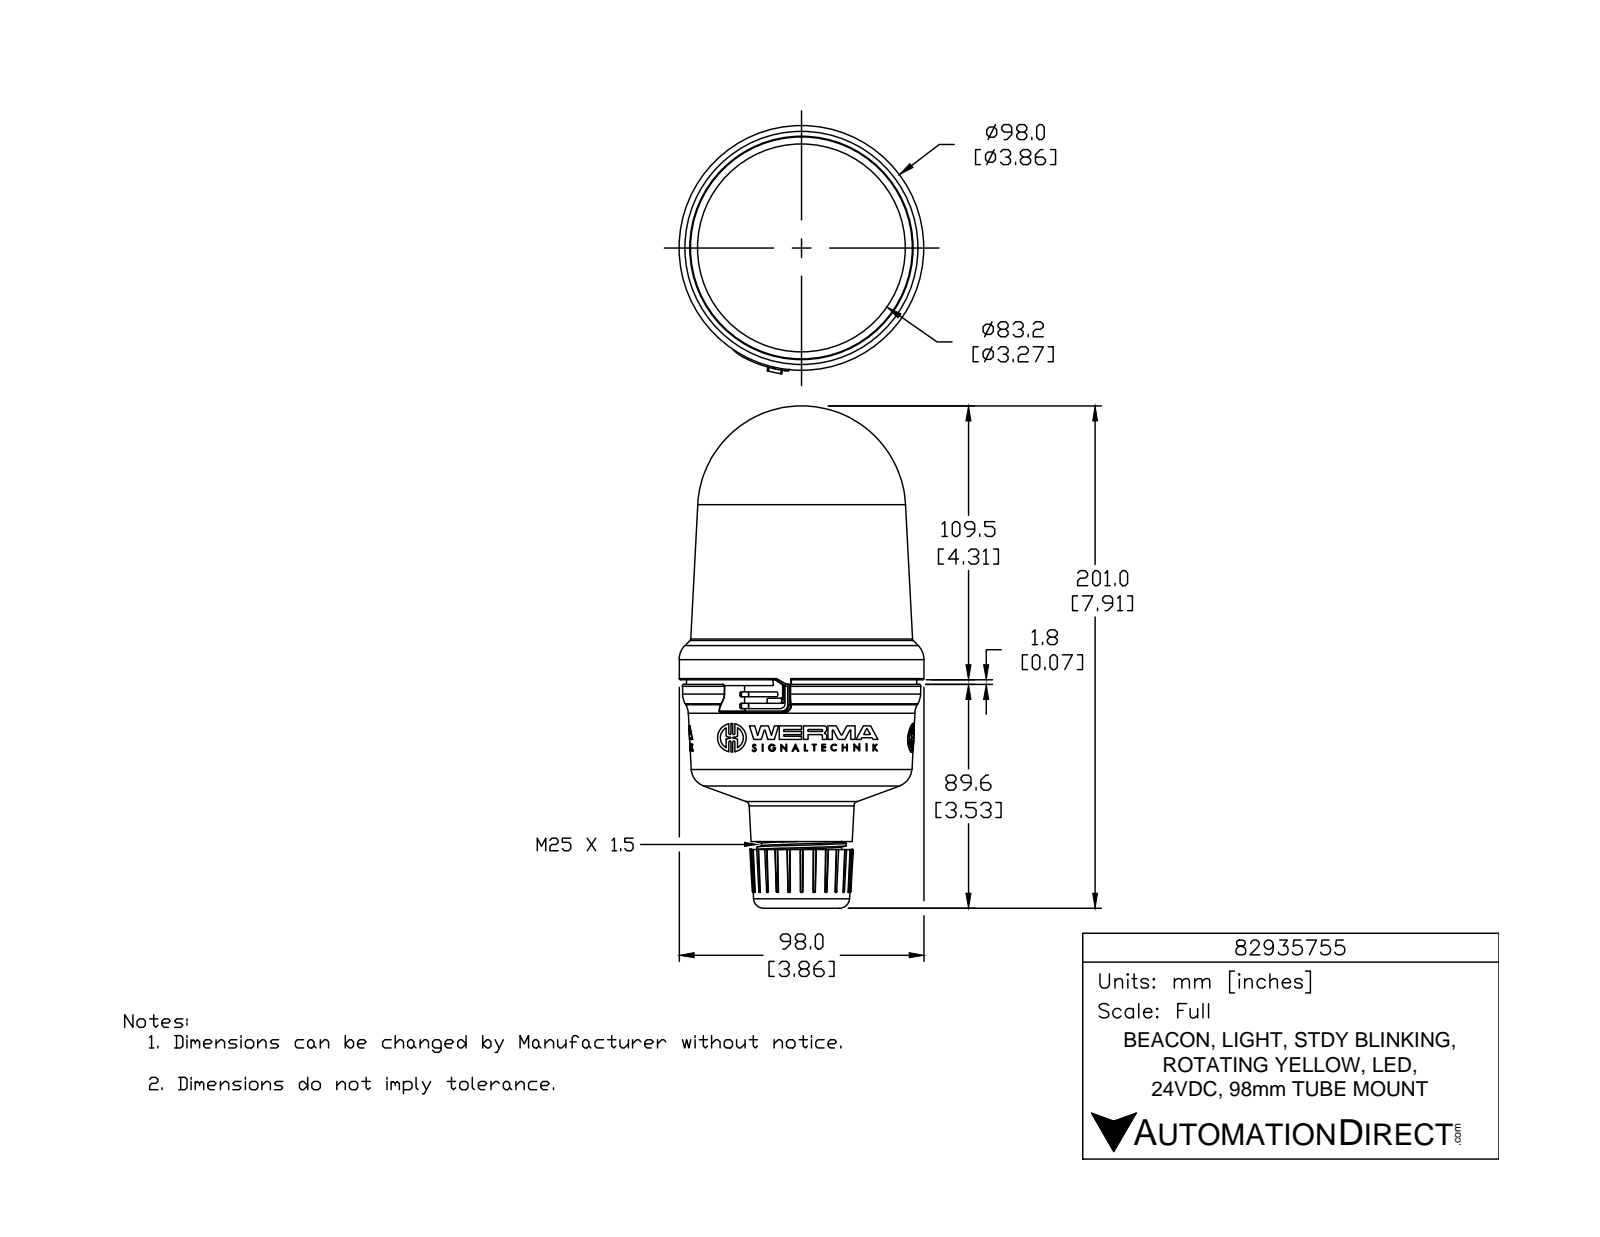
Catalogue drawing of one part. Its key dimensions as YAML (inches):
part_name: "82935755"
step_written_by: "SolidWorks 2015 (AUTOMOTIVE_DESIGN)"
units: inches
bodies: {solids: 1, faces: 1006, planar: 554, cylindrical: 189, other: 263}
overall_size: [7.914, 3.912, 3.858]
volume: 54.7
surface_area: 91.39
round_holes:
  - {diameter: 0.078, count: 3}
  - {diameter: 1.013, count: 1}
  - {diameter: 1.024, count: 1}
round_bosses_or_shafts:
  - {diameter: 0.452, count: 3}
  - {diameter: 0.113, count: 3}
  - {diameter: 3.858, count: 1}
  - {diameter: 1.409, count: 1}
  - {diameter: 1.261, count: 1}
partial_cylinders:
  - {radius: 0.02, count: 12}
  - {radius: 0.007, count: 9}
  - {radius: 0.007, count: 6}
  - {radius: 0.016, count: 6}
  - {radius: 0.016, count: 6}
  - {radius: 0.016, count: 6}
  - {radius: 0.262, count: 6}
  - {radius: 0.006, count: 3}
face_to_face_distances: [2.214, 0.462, 2.676, 0.335, 0.127, 2.548, 2.603, 2.476, 2.141, 0.073]
